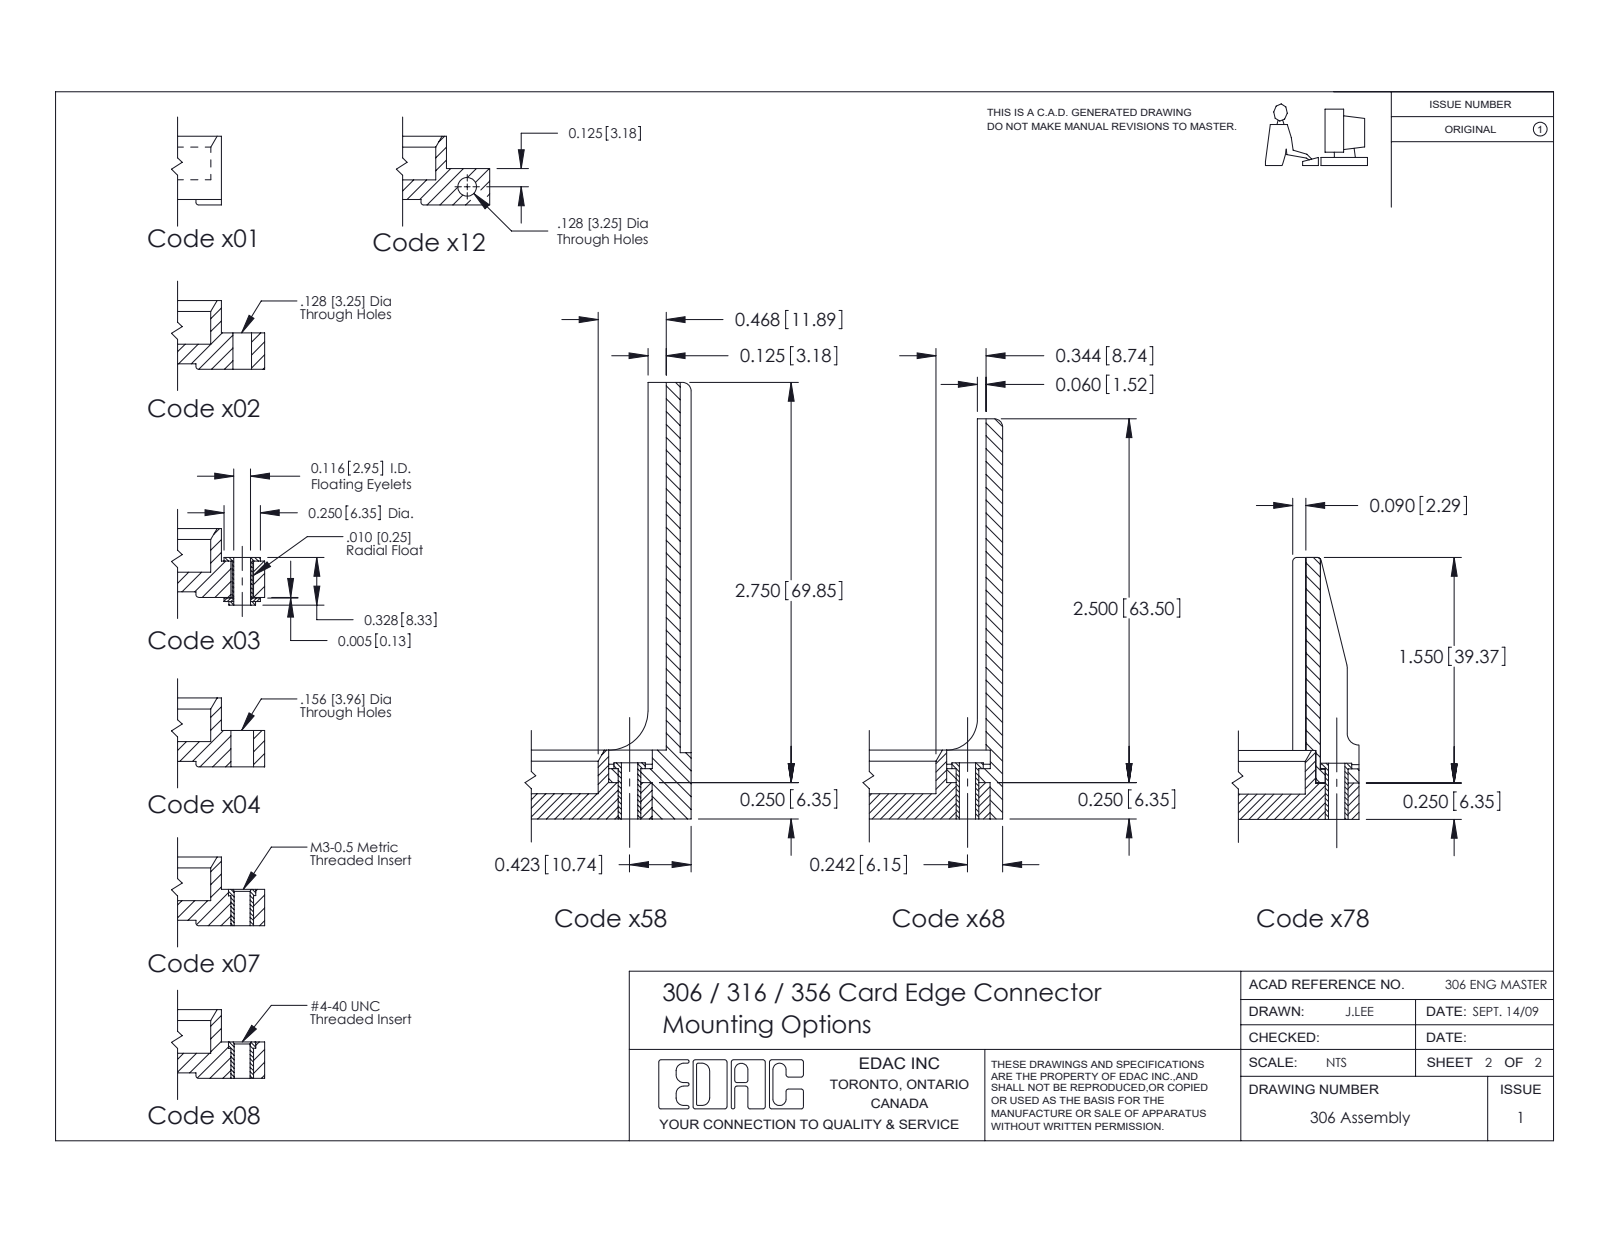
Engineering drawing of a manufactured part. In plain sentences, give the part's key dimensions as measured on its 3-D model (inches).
The part is named "306 Part_.156 Dia; 306-006-400-104; 306-290-001_100". Its 3-D file was written by "SolidWorks 2020 (CONFIG_CONTROL_DESIGN)". It is 7 solids with 586 faces: 382 planar, 180 cylindrical and 24 other. Overall it measures 1.842 by 0.743 by 0.343 inches. Its volume is 0.185 cubic inches and its surface area 6.132 square inches. Round holes: 2 of diameter 0.156. Partial cylindrical surfaces (rounded edges, fillets, slot ends): 23 of radius 0.015, 22 of radius 0.01, 12 of radius 0.024, 12 of radius 0.03, 6 of radius 0.007, 6 of radius 0.031, 3 of radius 0.026, 2 of radius 0.067. The main face-to-face distances are 0.343, 0.081, 0.261, 0.015, 0.156, 0.044, 0.03, 0.061, 0.031, 0.18. The hole center spacings are 1.532.
